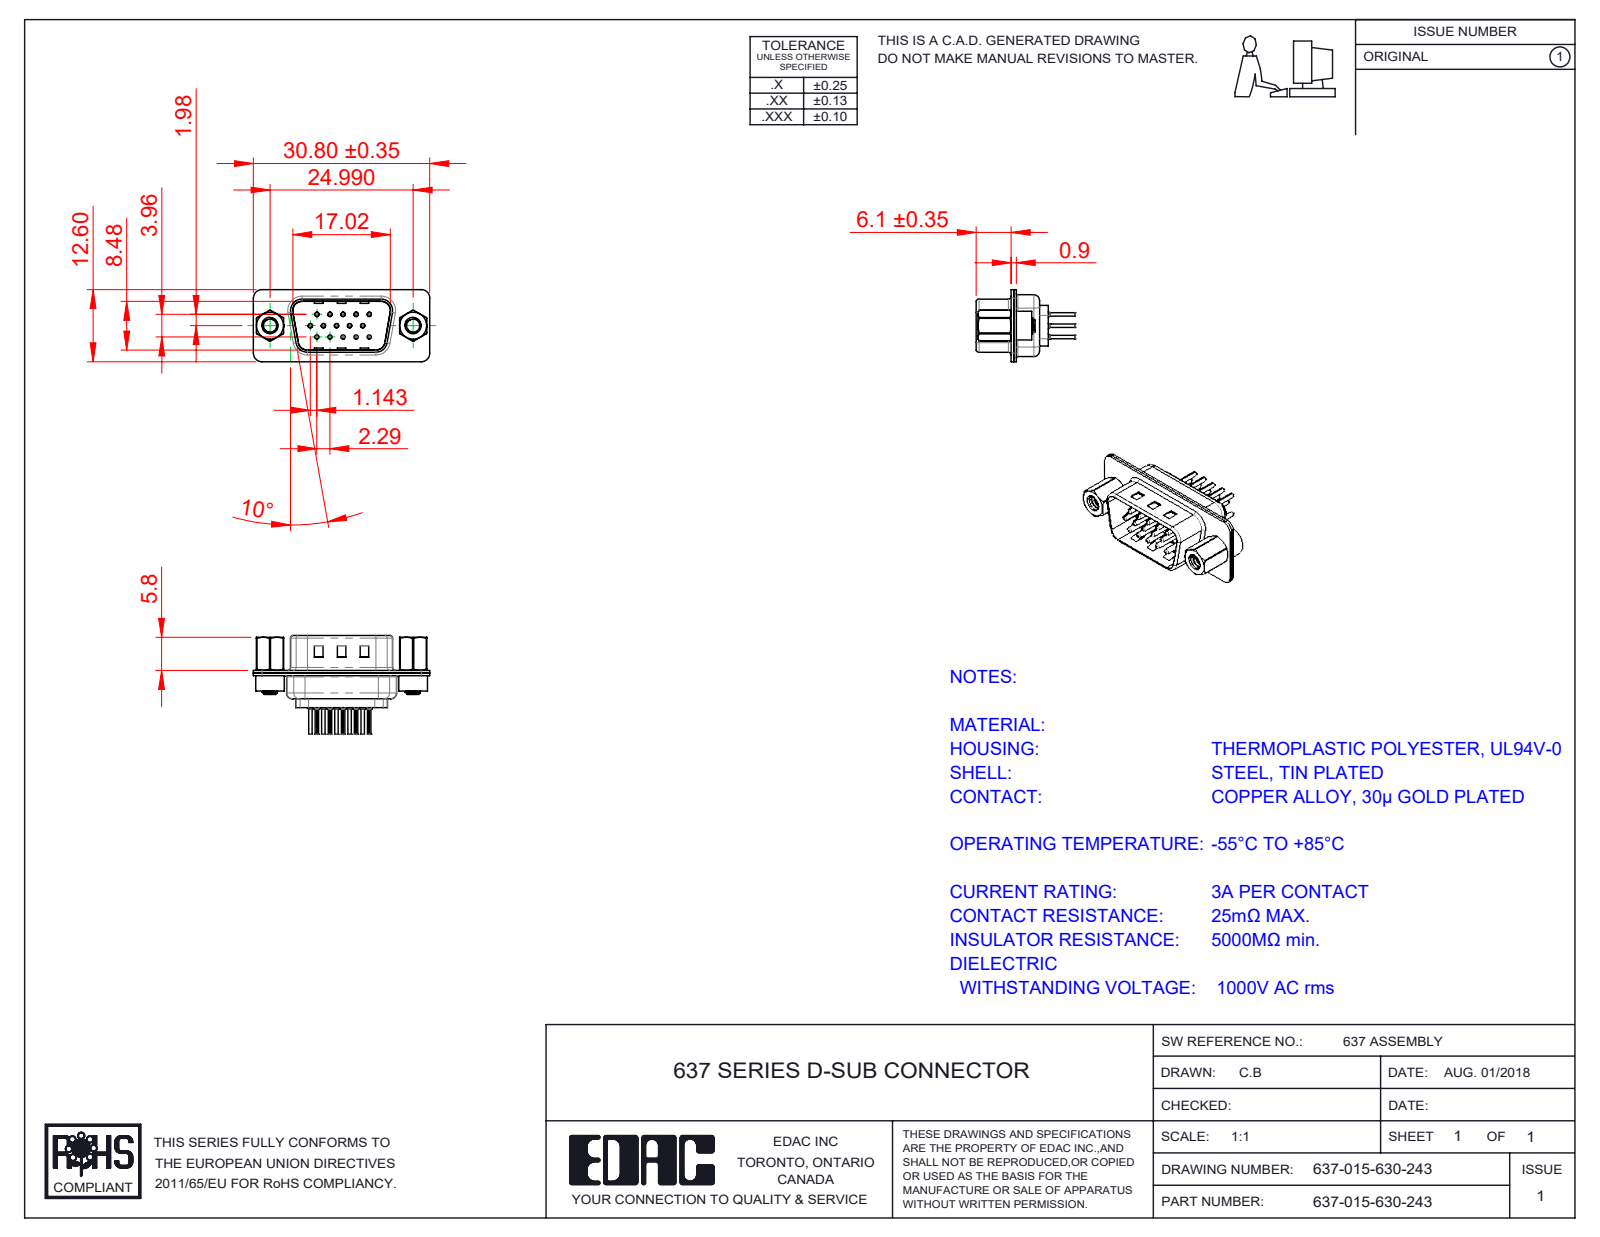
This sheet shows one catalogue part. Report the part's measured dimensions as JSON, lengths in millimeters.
{"part_name": "637-015-630-243; 637 4-40 Threaded Rivet; 637 Contact Row 2_30; 637 Contact Row 1_30 (+5 more)", "step_written_by": "SolidWorks 2020 (CONFIG_CONTROL_DESIGN)", "units": "millimeters", "bodies": {"solids": 22, "faces": 1930, "planar": 489, "cylindrical": 756, "other": 685}, "overall_size": [30.8, 17.25, 12.6], "volume_mm3": 1529, "surface_area_mm2": 5130, "round_holes": [[0.2, 15], [0.35, 15], [1.1, 15], [1.6, 15], [2.26, 2], [2.29, 2], [4, 2], [4.8, 2]], "round_bosses_or_shafts": [[2, 15], [1.5, 15], [0.75, 15], [0.6, 15], [5, 2], [4.9, 2], [2.79, 2]], "partial_cylinders_radius": [[0.1, 30], [1.5, 16], [2, 12], [0.5, 8], [0.25, 4], [0.55, 4], [0.7, 4], [0.95, 4]], "face_to_face_distances": [0.45, 0.9, 0.4, 0.7, 8.88, 8.48, 1.05, 0.31, 4.55, 6.5], "hole_center_spacings": [3.96, 2.28, 4.57, 2.29, 6.05, 6.86, 7.92, 6.04]}
